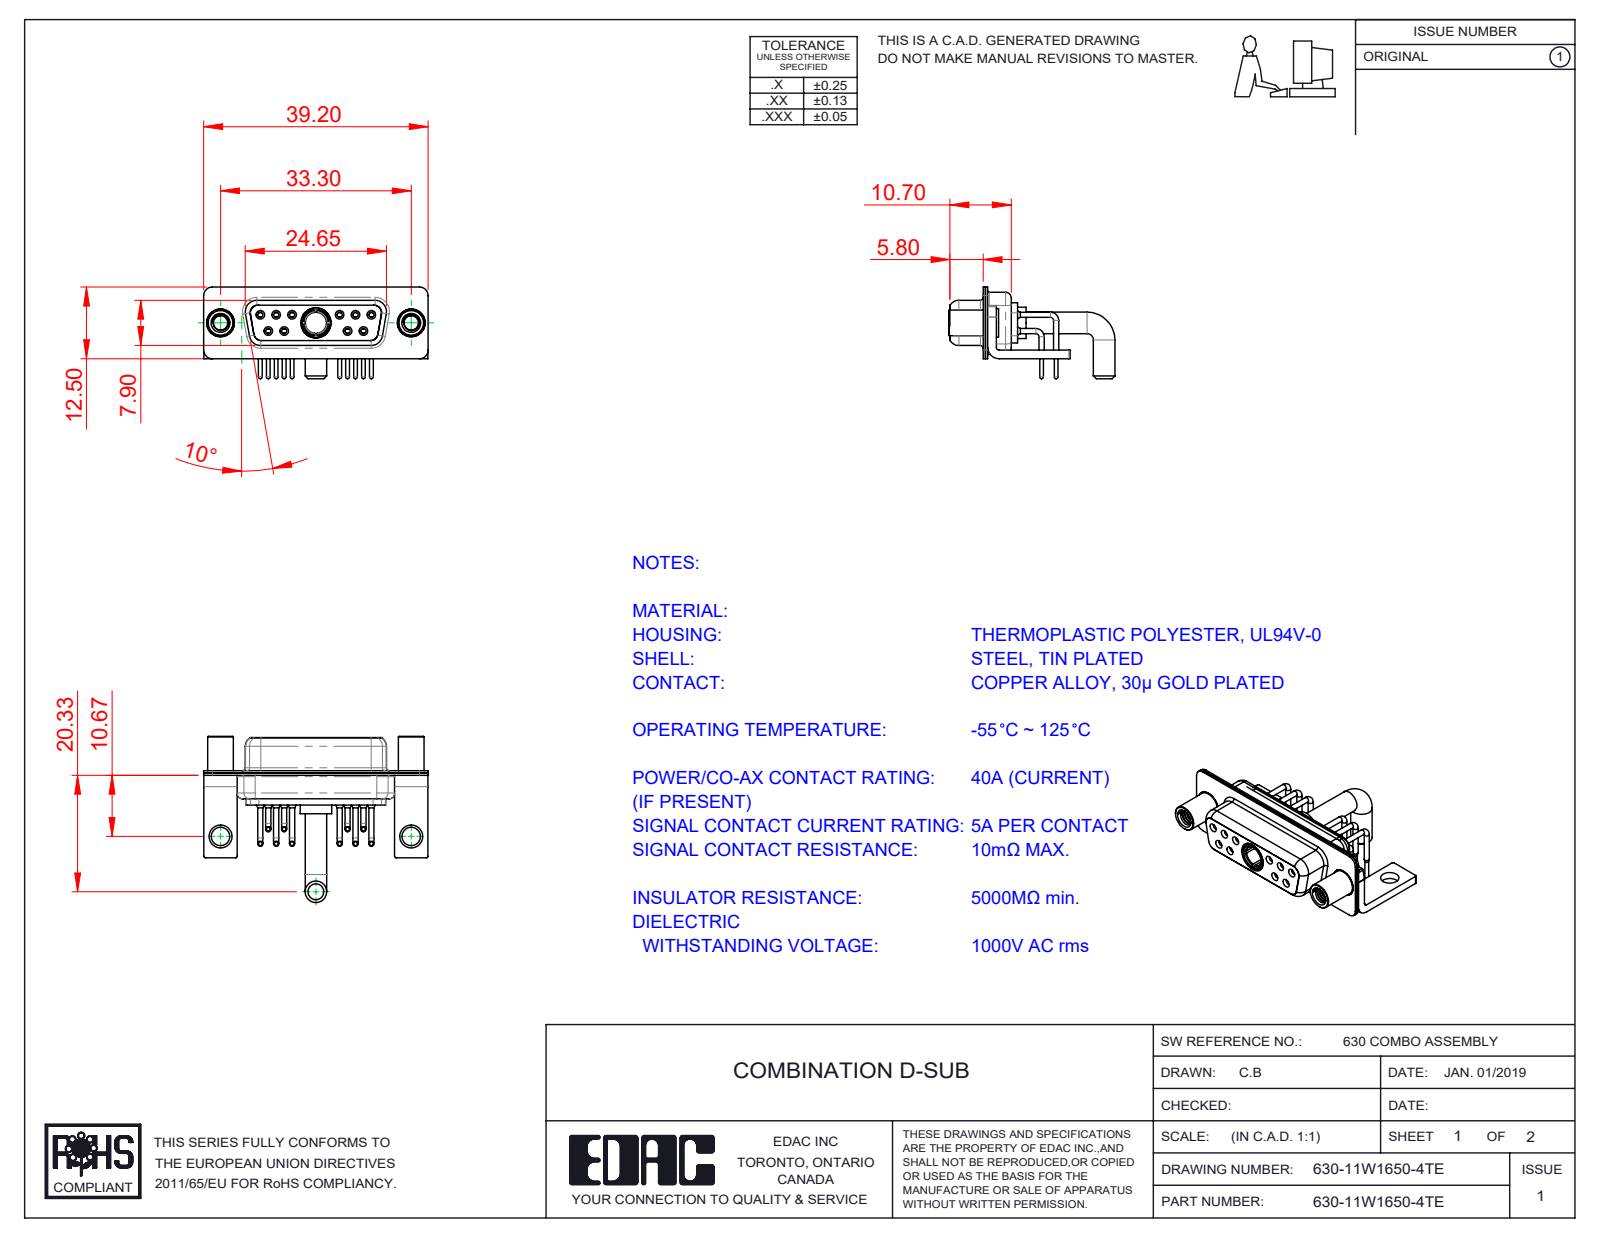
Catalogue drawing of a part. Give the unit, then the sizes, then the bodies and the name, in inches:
Units: inches
Overall size (bounding box): 1.543 × 1.142 × 0.63
Round holes (diameter × count): ⌀0.035 ×10, ⌀0.043 ×10, ⌀0.059 ×10, ⌀0.079 ×10, ⌀0.067 ×6, ⌀0.063 ×4, ⌀0.191 ×3, ⌀0.098 ×2, ⌀0.126 ×2, ⌀0.157 ×2, ⌀0.159 ×2, ⌀0.146 ×1
Round bosses / shafts (diameter × count): ⌀0.035 ×10, ⌀0.026 ×10, ⌀0.063 ×6, ⌀0.197 ×2, ⌀0.195 ×2, ⌀0.189 ×2, ⌀0.177 ×2, ⌀0.148 ×2
Partial cylindrical surfaces — rounded edges, fillets, slot ends (radius × count): R0.01 ×16, R0.059 ×16, R0.079 ×13, R0.053 ×12, R0.063 ×8, R0.02 ×5, R0.024 ×4, R0.026 ×4
Main face-to-face distances: 0.016, 0.031, 0.055, 0.018, 0.333, 0.059, 0.071, 0.35, 0.244, 0.091
Hole centre spacings: 0.124, 0.109, 0.545, 0.436, 0.654, 0.198, 0.198, 0.218
Volume: 0.194 in³ · Surface area: 11.35 in²
Bodies: 19 solids, 985 faces (268 planar, 464 cylindrical, 253 other)
Part name (STEP PRODUCT): Power Socket_Ext 40A RA; 630Combo Contact Row 2; 630-11W1650-4TE; 630Combo Housing_11W1 (+5 more)
STEP written by: SolidWorks 2020 (CONFIG_CONTROL_DESIGN)
